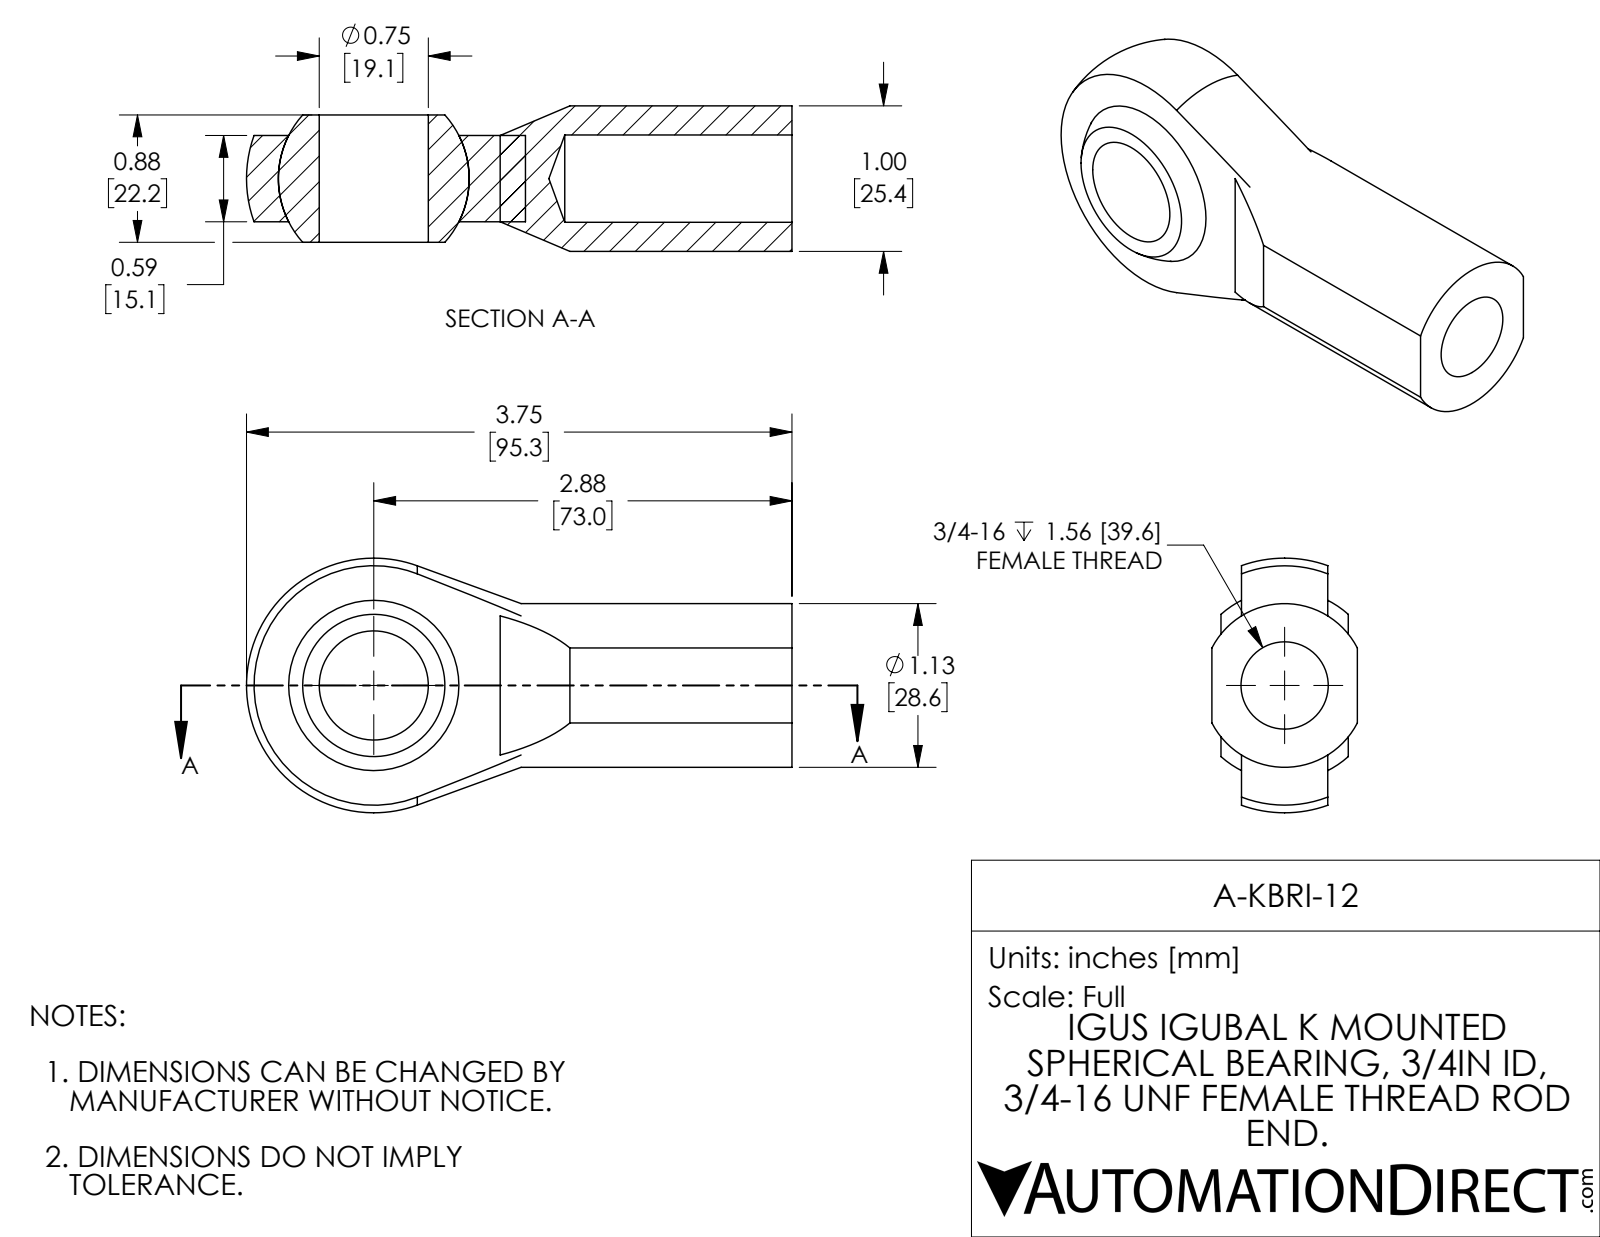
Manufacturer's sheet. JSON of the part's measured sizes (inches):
{"part_name": "A-KBRI-12", "step_written_by": "SolidWorks 2017 (AUTOMOTIVE_DESIGN)", "units": "inches", "bodies": {"solids": 3, "faces": 30, "planar": 11, "cylindrical": 7, "other": 12}, "overall_size": [3.715, 1.75, 1], "volume_in3": 2.83, "surface_area_in2": 26.66, "round_holes": [[0.6, 1], [0.75, 1]], "partial_cylinders_radius": [[0.562, 1]], "face_to_face_distances": [0.204, 0.796, 0.593, 1, 2.006, 1.832, 0.174, 0.063, 0.937, 0.141]}
